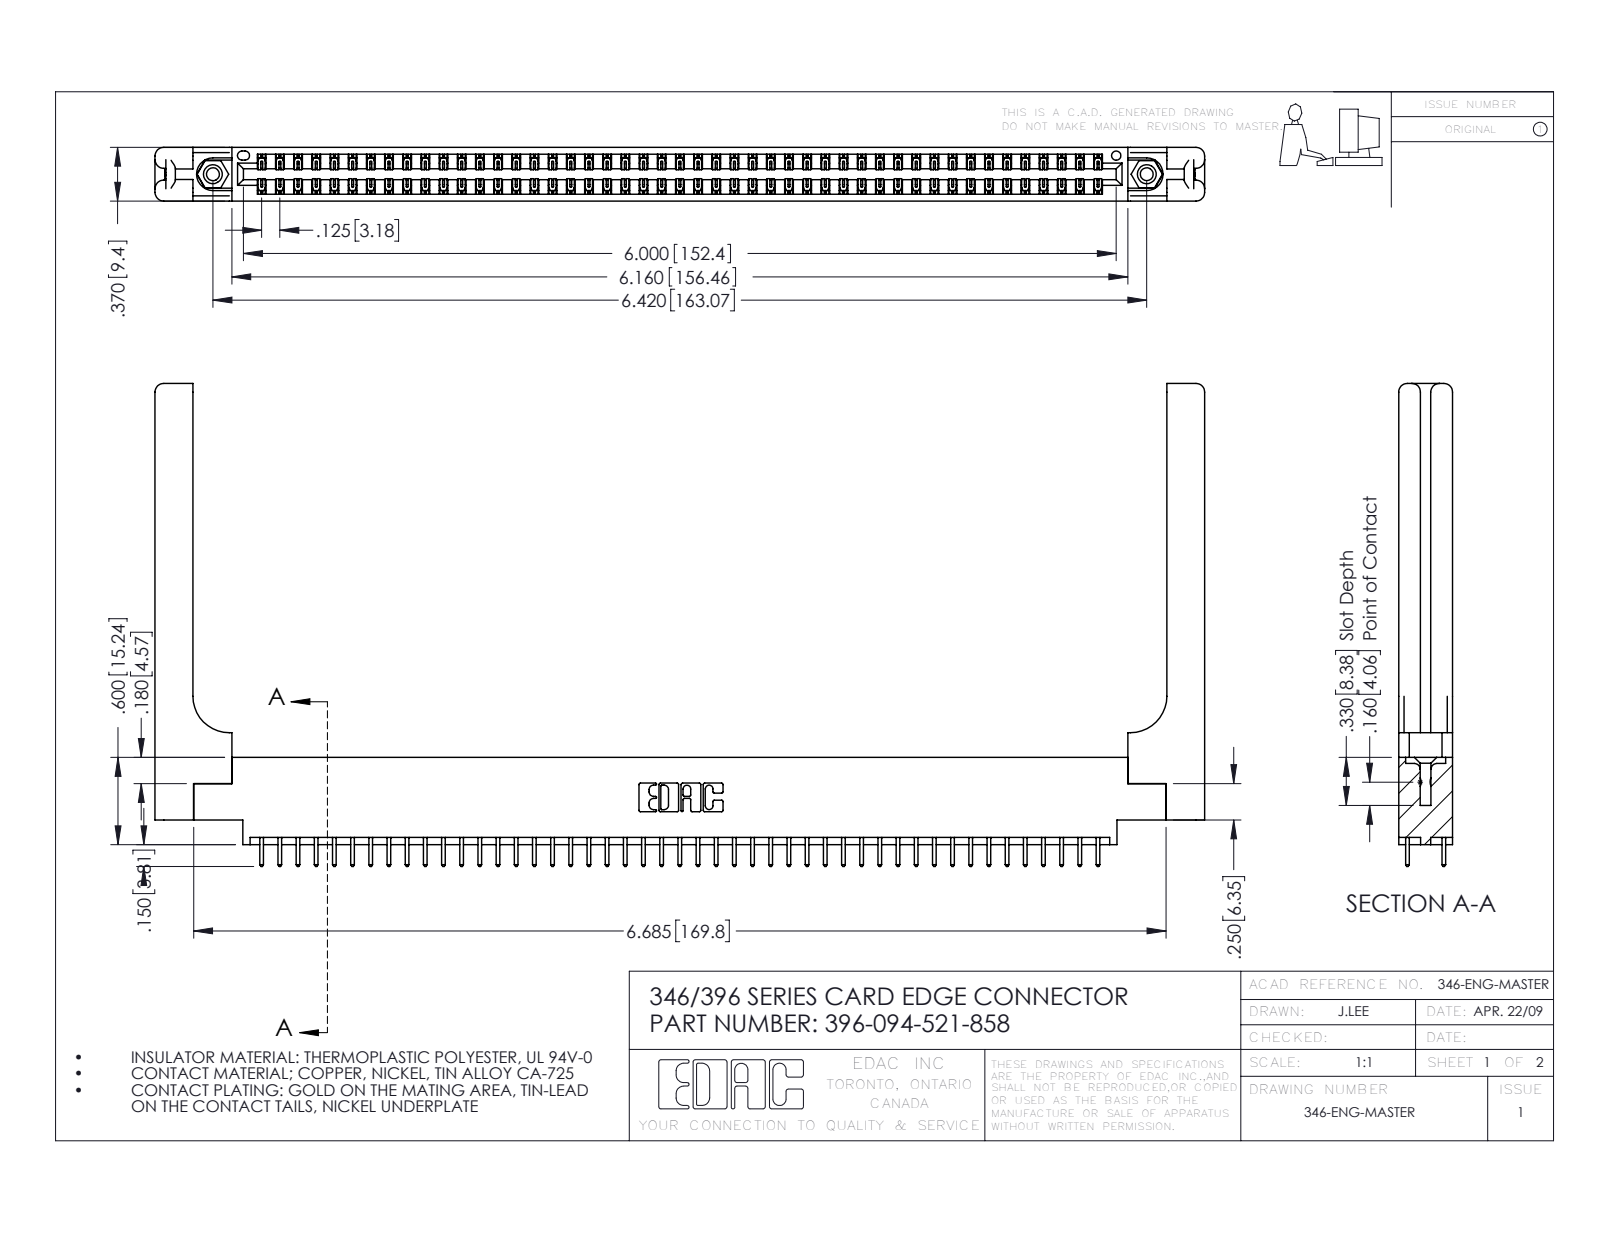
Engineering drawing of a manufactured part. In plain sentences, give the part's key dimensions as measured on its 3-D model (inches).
The part is named "396-094-521-858; 345-292-001_345-293-121; 346 Part_0.170 Offset - 0.156 Dia-TH; 345-250-001_345-250-001-102 (+1 more)". Its 3-D file was written by "SolidWorks 2016 (CONFIG_CONTROL_DESIGN)". It is 99 solids with 5270 faces: 3518 planar, 1692 cylindrical and 60 other. Overall it measures 7.216 by 3.32 by 0.37 inches. Its volume is 1.539 cubic inches and its surface area 45.46 square inches. Round holes: 2 of diameter 0.089, 2 of diameter 0.125, 2 of diameter 0.156, 1 of diameter 0.064. Round bosses or shafts: 2 of diameter 0.155. Partial cylindrical surfaces (rounded edges, fillets, slot ends): 141 of radius 0.006, 94 of radius 0.01, 22 of radius 0.01, 16 of radius 0.06, 6 of radius 0.007, 6 of radius 0.031, 3 of radius 0.026, 2 of radius 0.014. The main face-to-face distances are 0.37, 0.048, 0.322, 0.072, 0.25, 0.148, 0.15, 0.025, 0.298, 0.275. The hole center spacings are 0.246, 6.211, 6.42.
